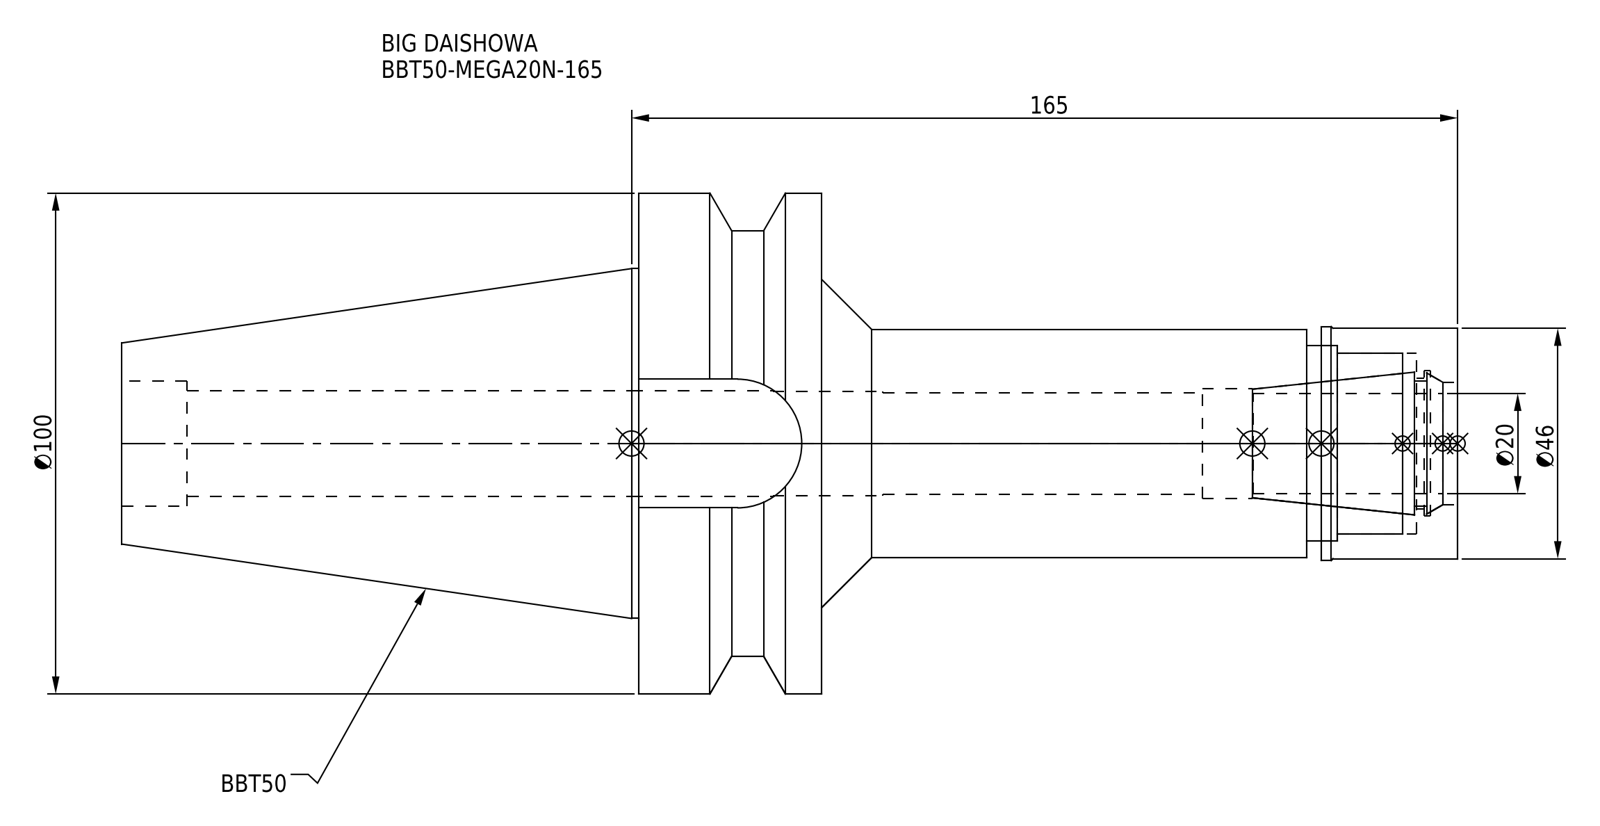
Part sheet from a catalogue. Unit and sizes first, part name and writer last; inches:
Units: inches
Overall size (bounding box): 10.504 × 3.937 × 3.937
Round holes (diameter × count): ⌀0.799 ×1, ⌀0.819 ×1, ⌀0.835 ×1, ⌀0.866 ×1, ⌀0.965 ×1, ⌀0.984 ×1, ⌀1.024 ×1, ⌀1.142 ×1, ⌀1.417 ×1, ⌀1.535 ×1
Round bosses / shafts (diameter × count): ⌀3.937 ×1, ⌀3.346 ×1, ⌀2.75 ×1, ⌀1.839 ×1, ⌀1.811 ×1, ⌀1.791 ×1
Partial cylindrical surfaces — rounded edges, fillets, slot ends (radius × count): R0.506 ×1
Main face-to-face distances: 1.437, 5, 6.437, 10.504, 5.504, 4.067, 2.787, 1.071, 3.929, 5.366
Volume: 37.35 in³ · Surface area: 134.3 in²
Bodies: 2 solids, 79 faces (23 planar, 42 cylindrical, 14 other)
Part name (STEP PRODUCT): MGN20_1.stp; BBT50MN20165-200_ASM.stp; BBT50-MEGA20N-165-200.stp; BBT50-MEGA20N-165 (+3 more)
STEP written by: SolidWorks 2019 (CONFIG_CONTROL_DESIGN)
